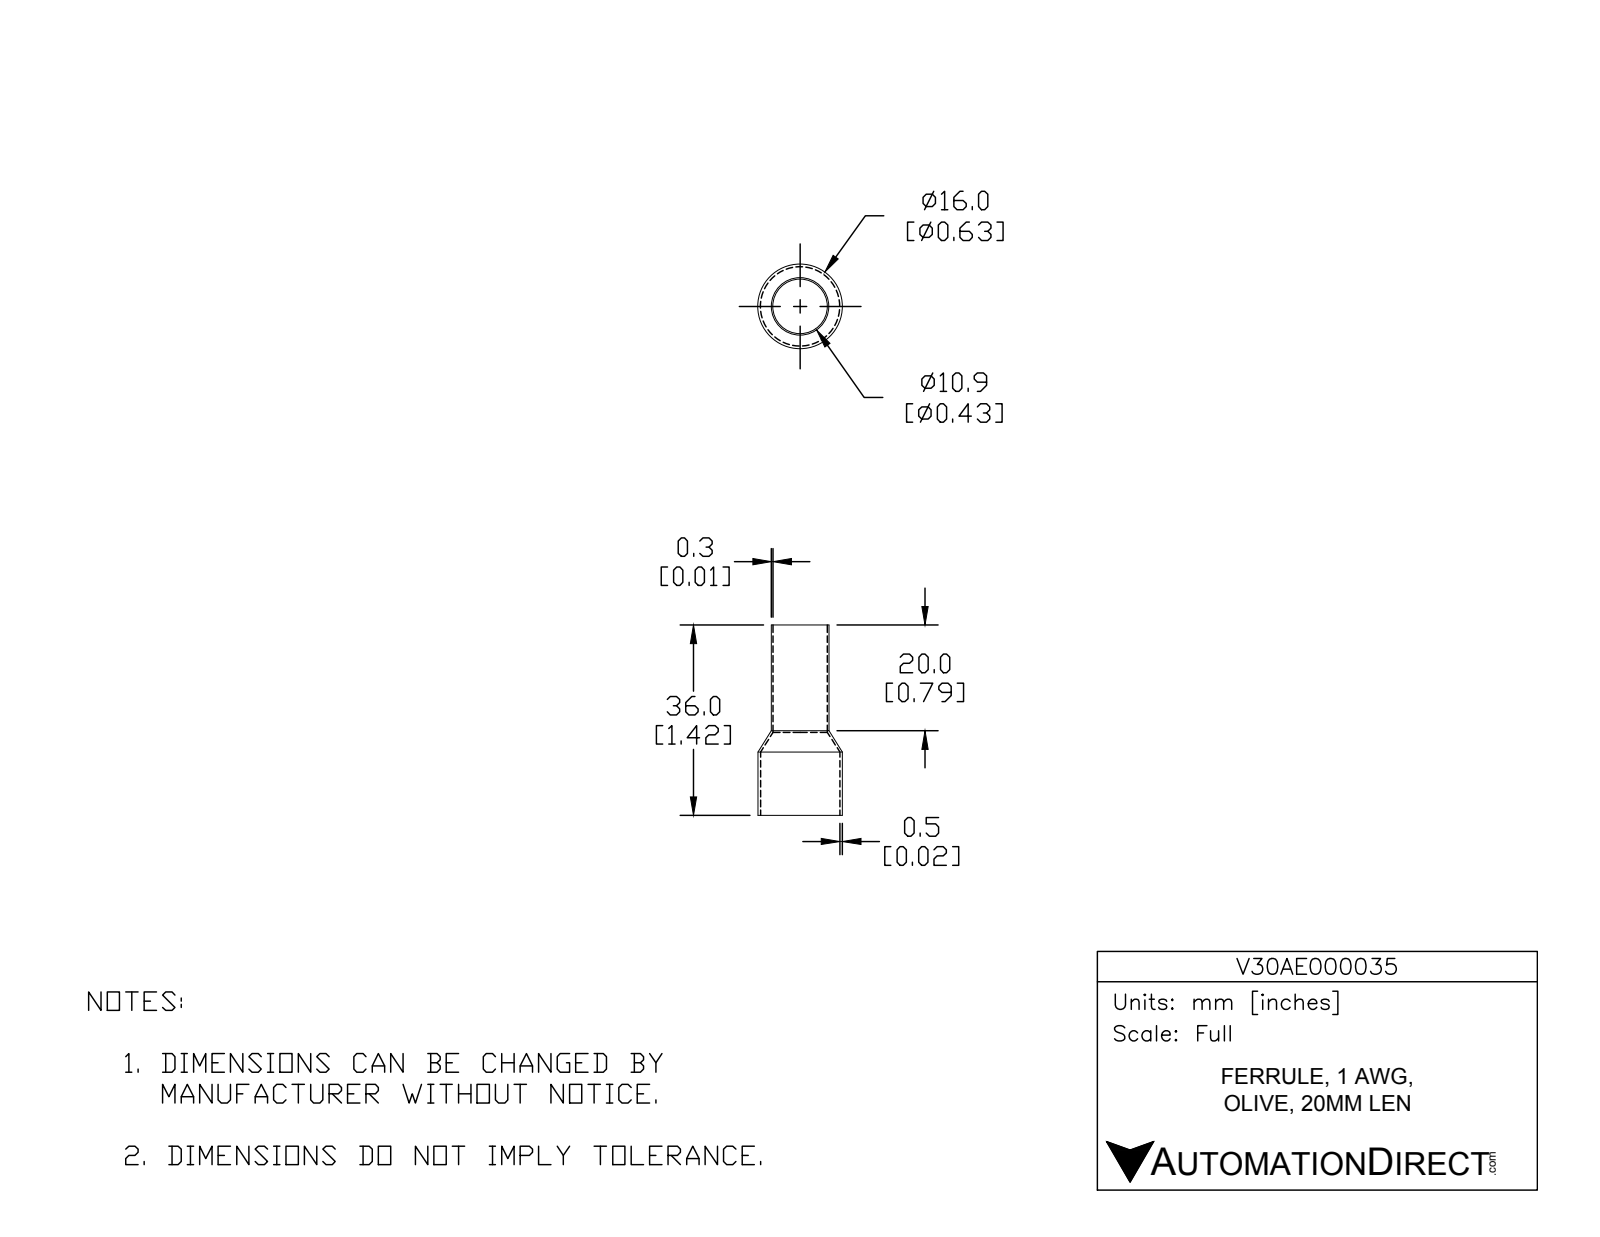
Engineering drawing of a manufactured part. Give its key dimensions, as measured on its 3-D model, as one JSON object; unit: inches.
{"part_name": "V30AE000035", "step_written_by": "SolidWorks 2017 (AUTOMOTIVE_DESIGN)", "units": "inches", "bodies": {"solids": 1, "faces": 14, "planar": 2, "cylindrical": 8, "other": 4}, "overall_size": [1.417, 0.63, 0.63], "volume_in3": 0.035, "surface_area_in2": 4.524, "round_holes": [[0.406, 1], [0.591, 1]], "round_bosses_or_shafts": [[0.63, 1], [0.429, 1]], "face_to_face_distances": [1.417]}
